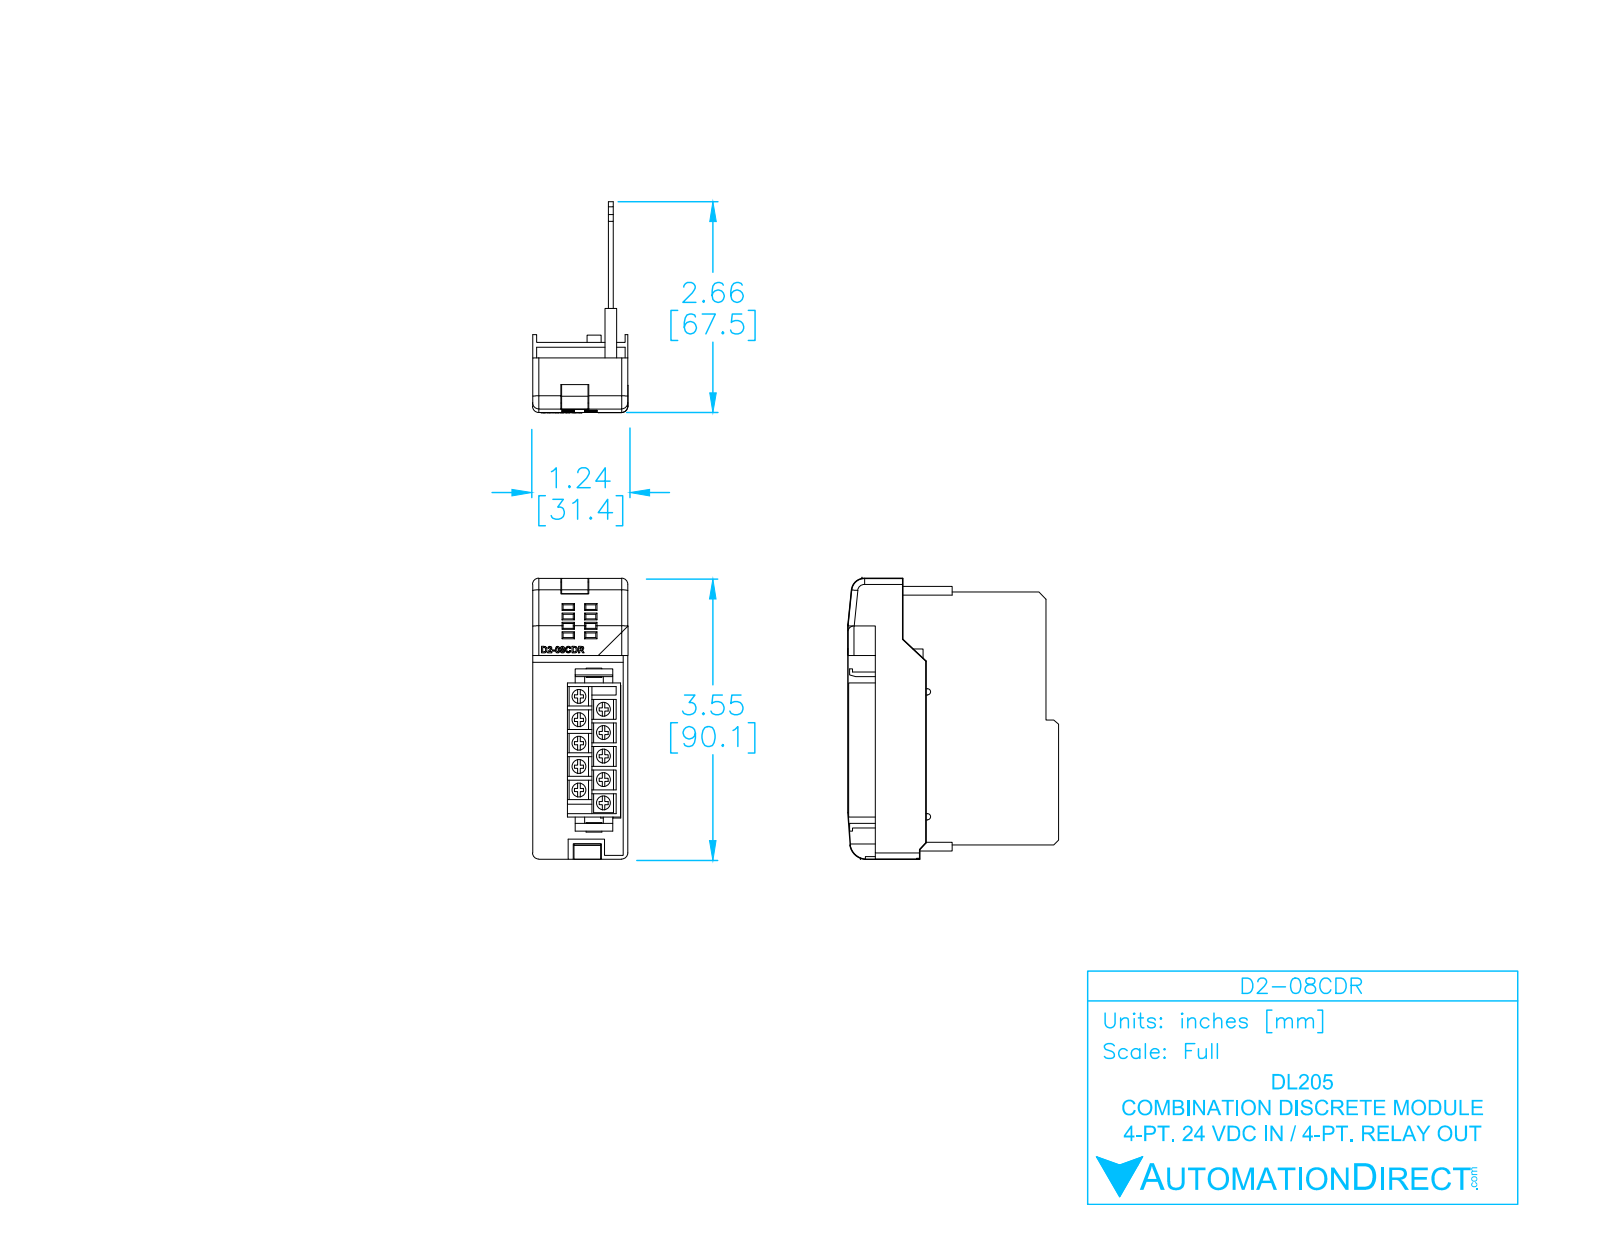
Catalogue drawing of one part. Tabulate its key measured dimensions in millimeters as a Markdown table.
| quantity | value |
| --- | --- |
| part name | D2-08CDR_ModuleCase_light_NEW |
| STEP written by | SolidWorks 2009 (AUTOMOTIVE_DESIGN) |
| units | millimeters |
| bodies | 6 solids, 593 faces (401 planar, 75 cylindrical, 117 other) |
| overall size | 90 × 67.56 × 30.55 |
| volume | 25 374 mm³ |
| surface area | 28 533 mm² |
| round bosses / shafts (diameter × count) | 4.5 × 10 |
| partial cylindrical surfaces (radius × count) | 0.35 × 16, 2 × 9, 0.25 × 2, 1 × 2, 1.25 × 2, 4.12 × 1, 5.39 × 1 |
| main face-to-face distances | 1.5, 4.72, 6.22, 2.37, 3.87, 2.35, 3.22, 0.85, 8.14, 24.28 |
